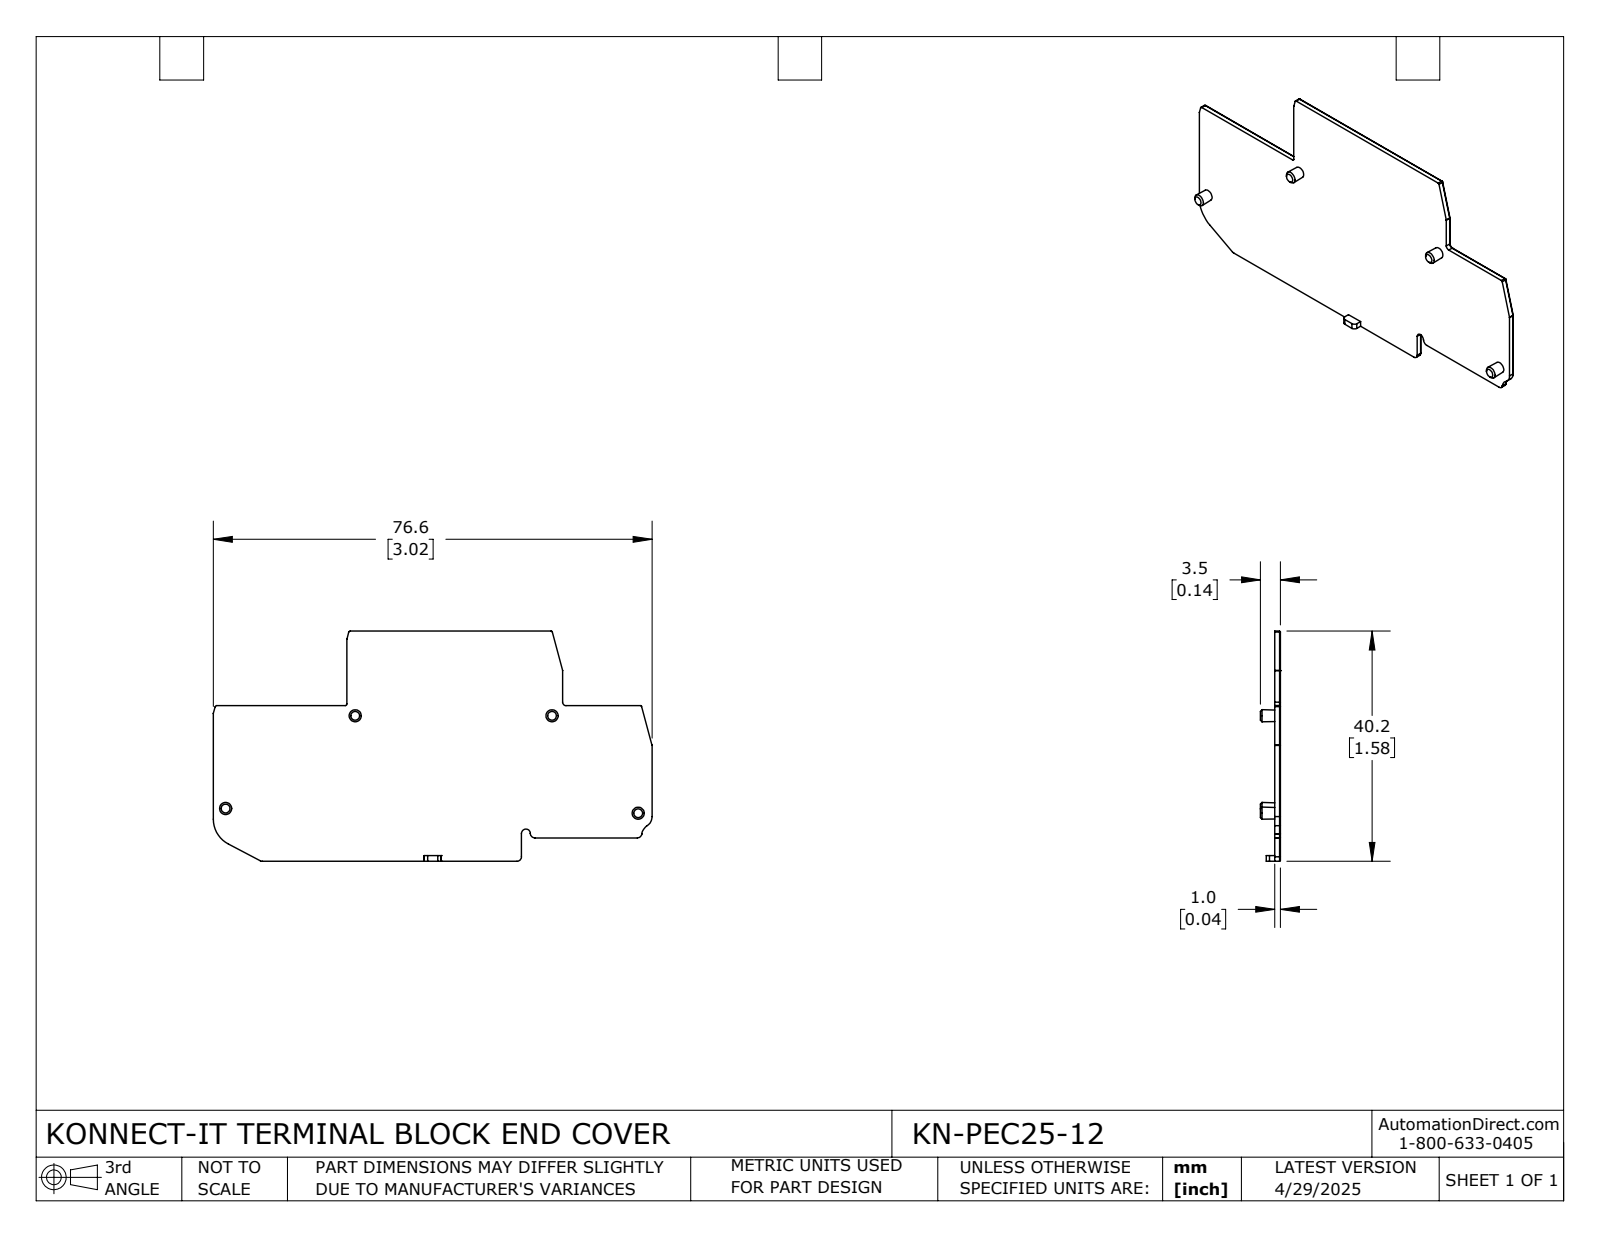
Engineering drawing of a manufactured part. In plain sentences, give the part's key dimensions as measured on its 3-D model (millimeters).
The part is named "KN-PEC25-12". Its 3-D file was written by "SolidWorks 2024 (CONFIG_CONTROL_DESIGN)". It is 1 solid with 99 faces: 45 planar, 38 cylindrical and 16 other. Overall it measures 76.6 by 40.2 by 3.5 millimeters. Its volume is 2 470 cubic millimeters and its surface area 5 177 square millimeters. Partial cylindrical surfaces (rounded edges, fillets, slot ends): 8 of radius 0.2, 6 of radius 0.3, 5 of radius 0.7, 4 of radius 0.8, 3 of radius 0.1, 3 of radius 0.6, 1 of radius 0.4, 1 of radius 0.8. The main face-to-face distances are 1, 13, 27.2, 40.2, 0.8, 4.1, 23.1, 36.1, 27.1, 40.1.
